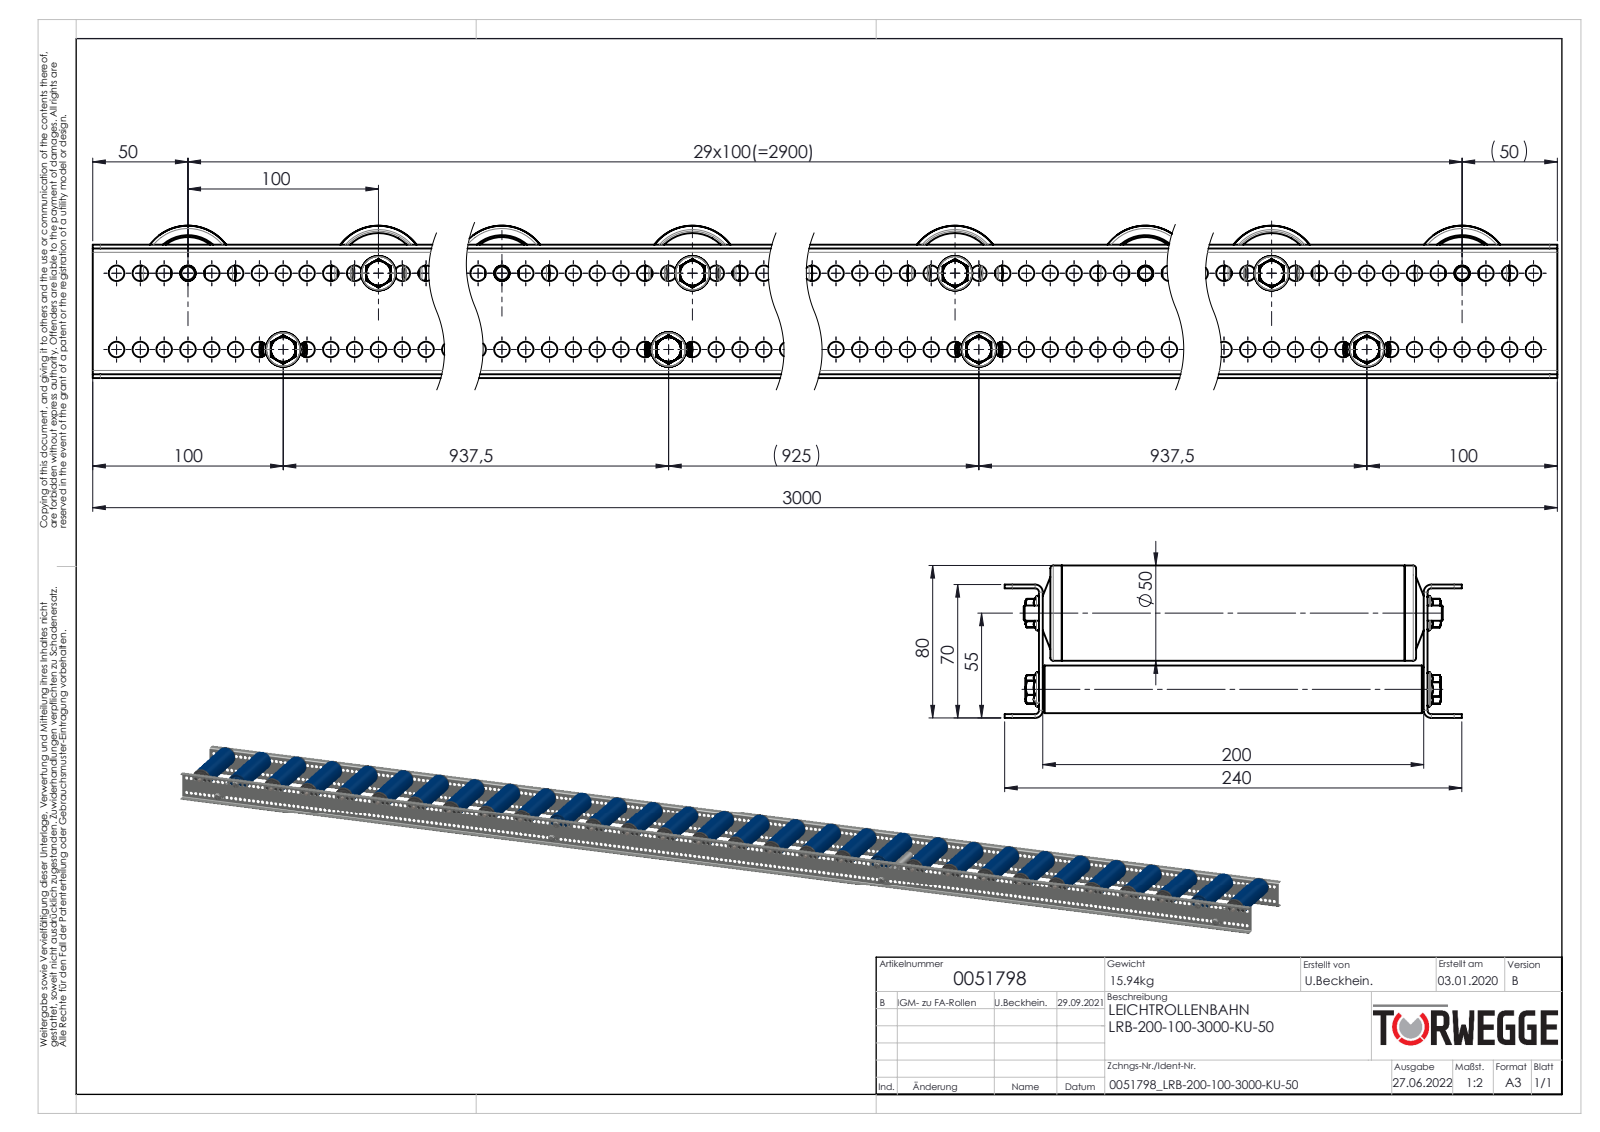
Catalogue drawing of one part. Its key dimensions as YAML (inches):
part_name: "0039780-Achse-ST-Ø12-KFG_IGM8-AL=200; 0026266_Typ-KUT100-50x2,8-12; 0026267_Typ-KUT100-50x2,8-8_Lageboden-schematisch; S100994_Sperrzahnschraube_M08x16-8.8-A2K (+8 more)"
step_written_by: "SolidWorks 2020 (AUTOMOTIVE_DESIGN)"
units: inches
bodies: {solids: 529, faces: 10386, planar: 2510, cylindrical: 4836, other: 3040}
overall_size: [118.11, 9.449, 3.15]
volume: 341.1
surface_area: 6879
round_holes:
  - {diameter: 0.323, count: 478}
  - {diameter: 0.299, count: 26}
  - {diameter: 0.315, count: 26}
  - {diameter: 0.984, count: 26}
  - {diameter: 1.181, count: 26}
  - {diameter: 1.378, count: 26}
  - {diameter: 1.551, count: 26}
  - {diameter: 1.575, count: 26}
  - {diameter: 0.268, count: 8}
  - {diameter: 0.472, count: 4}
  - {diameter: 0.476, count: 4}
  - {diameter: 0.63, count: 4}
round_bosses_or_shafts:
  - {diameter: 1.969, count: 30}
  - {diameter: 1.748, count: 26}
  - {diameter: 1.496, count: 26}
  - {diameter: 1.417, count: 26}
  - {diameter: 1.299, count: 26}
  - {diameter: 0.866, count: 26}
  - {diameter: 0.827, count: 26}
  - {diameter: 0.984, count: 8}
partial_cylinders:
  - {radius: 0.024, count: 52}
  - {radius: 0.03, count: 52}
  - {radius: 0.096, count: 52}
  - {radius: 0.192, count: 26}
  - {radius: 0.276, count: 26}
  - {radius: 0.157, count: 8}
  - {radius: 0.079, count: 4}
face_to_face_distances: [0.079, 7.953, 2.677, 7.874, 8.031, 2.756, 2.598, 7.559, 0.236, 0.472]
hole_center_spacings: [0.492, 0.984, 1.476, 1.969, 2.461, 2.953, 3.445, 3.937]
